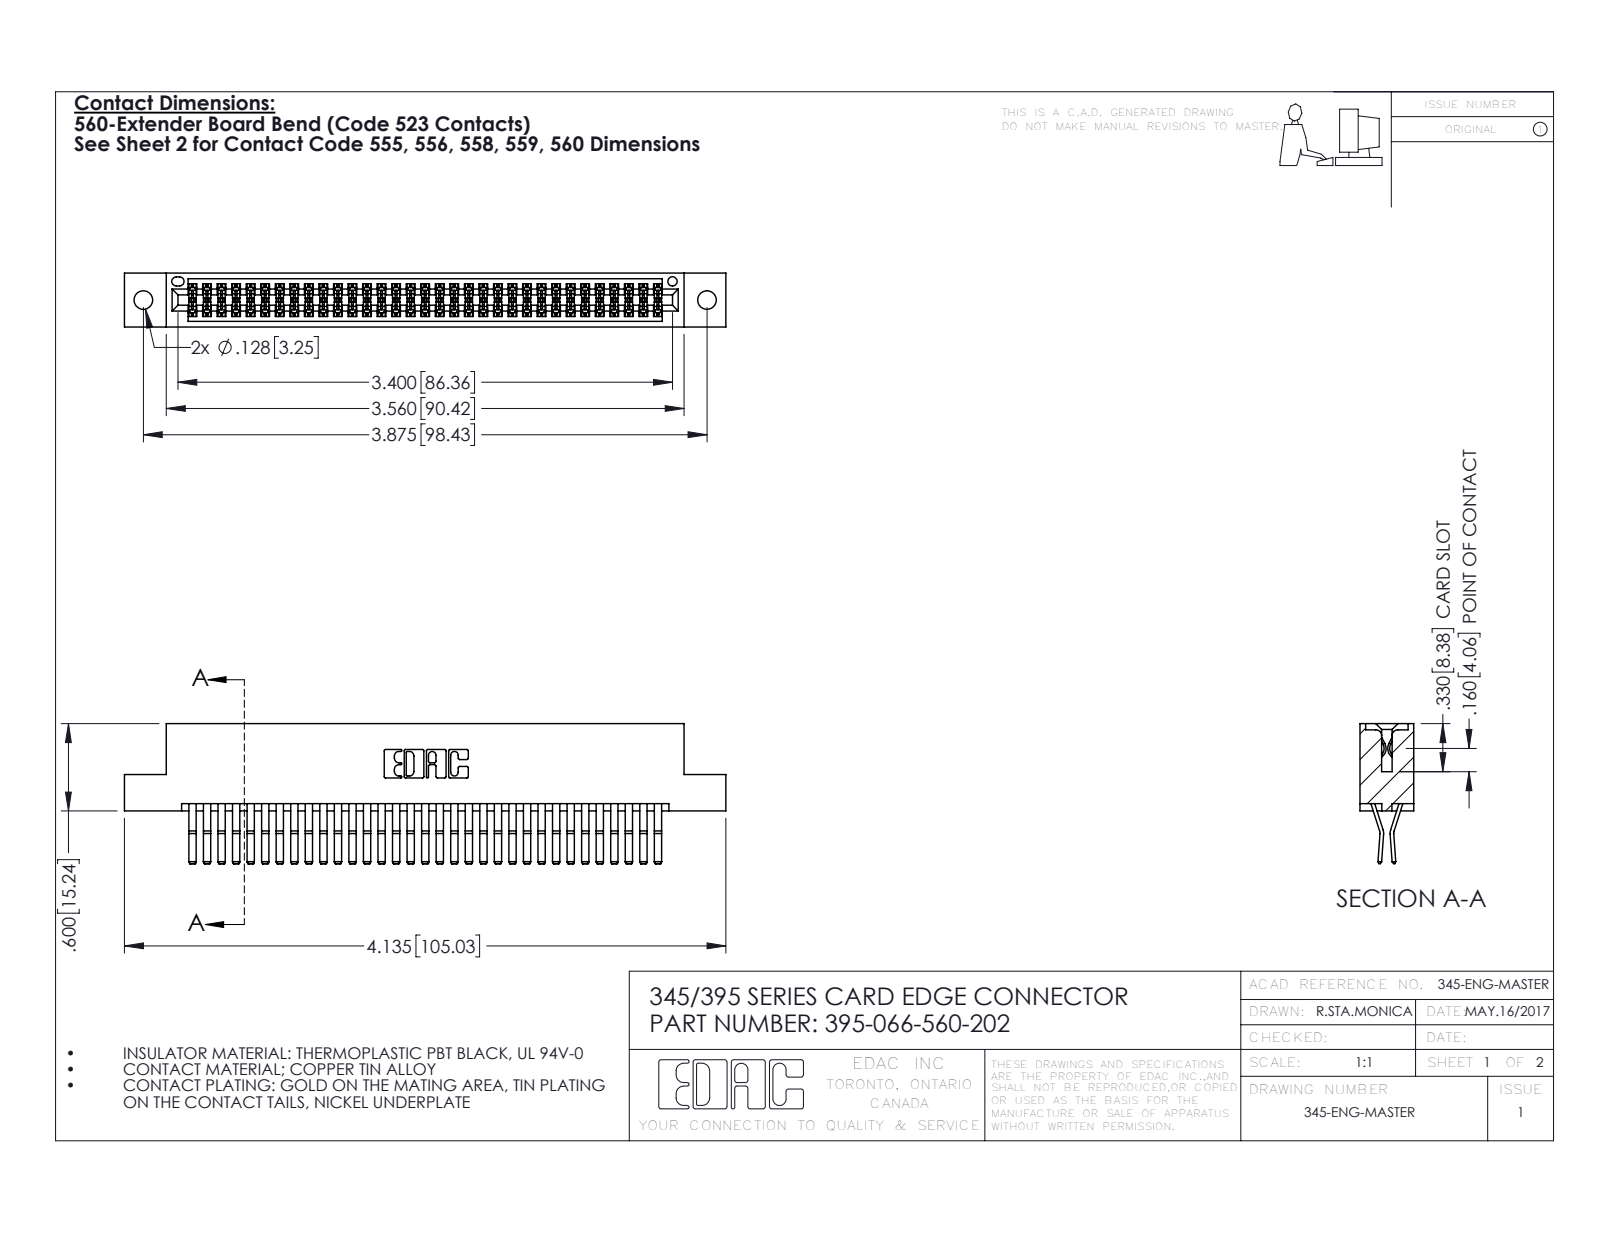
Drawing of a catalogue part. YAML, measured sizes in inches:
part_name: "345 Part_Flush Mounting Lugs - 0.128 Dia; 395-066-560-202; 345-292-001_560 Tail"
step_written_by: "SolidWorks 2016 (CONFIG_CONTROL_DESIGN)"
units: inches
bodies: {solids: 67, faces: 3558, planar: 2258, cylindrical: 1300, other: 0}
overall_size: [4.135, 0.962, 0.37]
volume: 0.642
surface_area: 25.12
round_holes:
  - {diameter: 0.128, count: 2}
  - {diameter: 0.064, count: 1}
partial_cylinders:
  - {radius: 0.006, count: 99}
  - {radius: 0.01, count: 22}
  - {radius: 0.007, count: 6}
  - {radius: 0.031, count: 6}
  - {radius: 0.026, count: 3}
  - {radius: 0.01, count: 2}
  - {radius: 0.014, count: 2}
  - {radius: 0.019, count: 2}
face_to_face_distances: [0.025, 0.298, 0.072, 0.2, 0.37, 0.098, 0.272, 0.225, 0.175, 0.149]
hole_center_spacings: [0.27, 3.64, 3.875]
